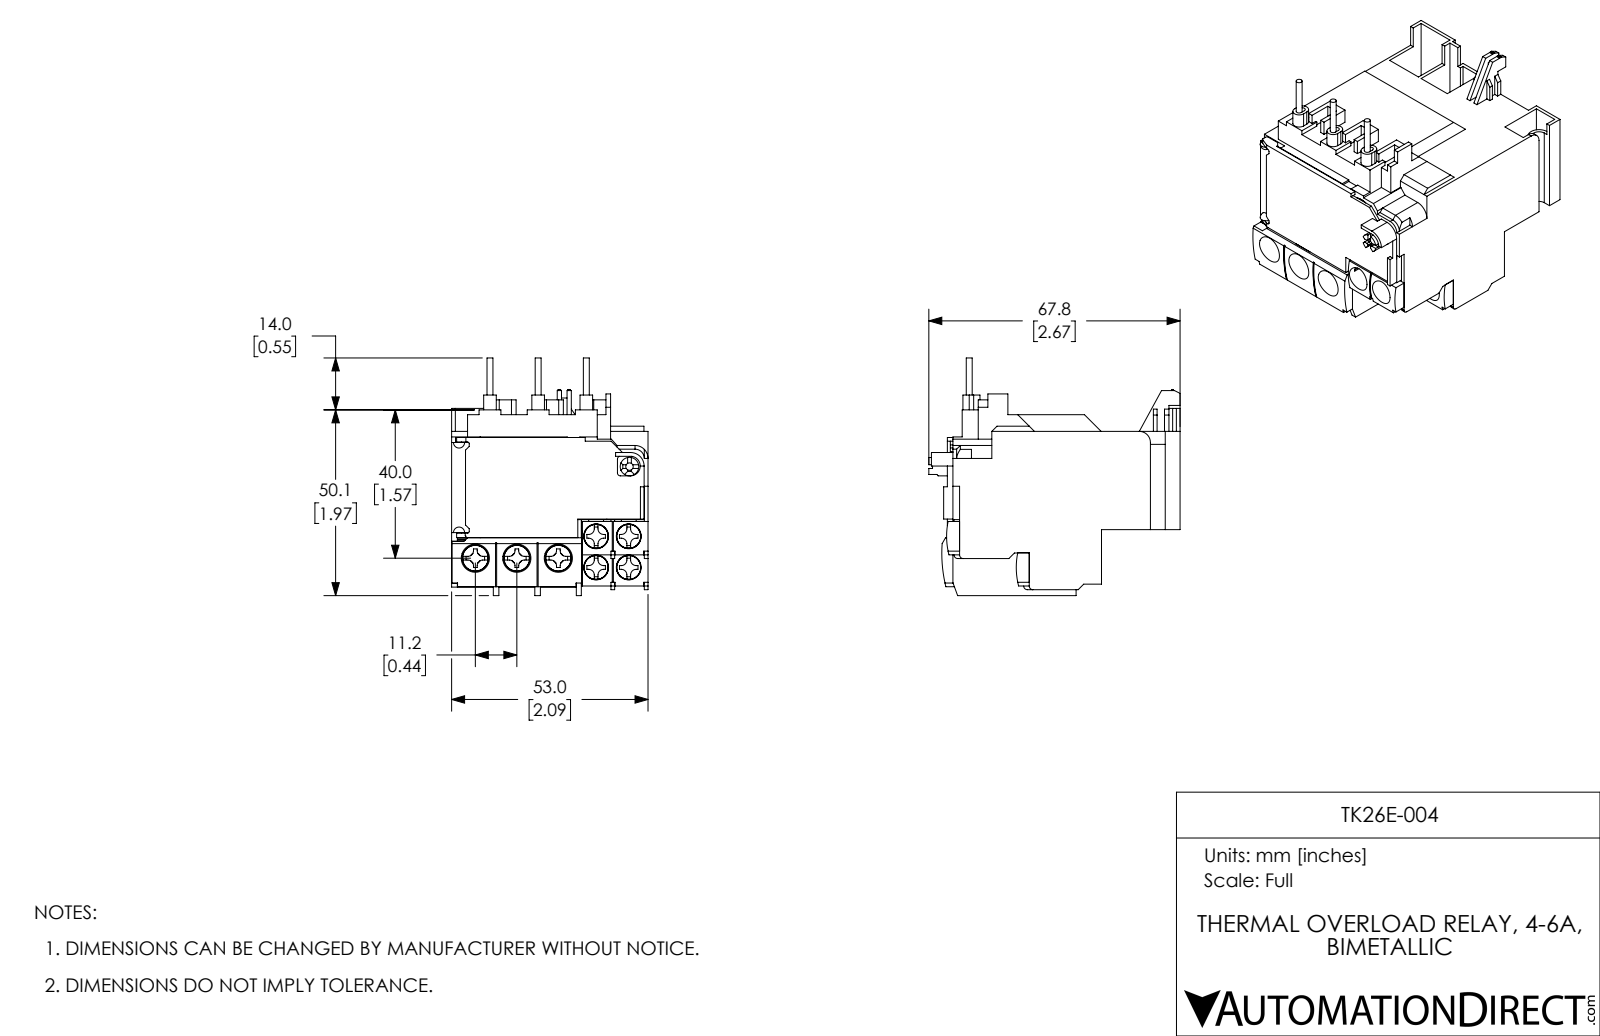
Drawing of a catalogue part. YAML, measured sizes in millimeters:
part_name: "TK26E-004"
step_written_by: "SolidWorks 2017 (AUTOMOTIVE_DESIGN)"
units: millimeters
bodies: {solids: 38, faces: 1480, planar: 1225, cylindrical: 220, other: 35}
overall_size: [67.8, 64.1, 53]
volume: 99940
surface_area: 38810
round_holes:
  - {diameter: 3.5, count: 4}
  - {diameter: 3.6, count: 4}
  - {diameter: 6.7, count: 4}
  - {diameter: 4, count: 3}
  - {diameter: 4.1, count: 3}
  - {diameter: 7.6, count: 3}
  - {diameter: 1, count: 1}
  - {diameter: 2, count: 1}
  - {diameter: 5, count: 1}
  - {diameter: 11, count: 1}
round_bosses_or_shafts:
  - {diameter: 6.6, count: 4}
  - {diameter: 1.6, count: 3}
  - {diameter: 6, count: 1}
partial_cylinders:
  - {radius: 1.5, count: 28}
  - {radius: 1, count: 8}
  - {radius: 0.5, count: 6}
  - {radius: 1.7, count: 6}
  - {radius: 0.8, count: 5}
  - {radius: 1.2, count: 4}
  - {radius: 4.3, count: 4}
  - {radius: 4.8, count: 3}
face_to_face_distances: [1, 9, 1.5, 12, 53, 2, 10, 11, 8.7, 0.7]
hole_center_spacings: [8.4, 8.8, 11.2, 12.2, 9.6, 10.5, 11.8, 18.8]
